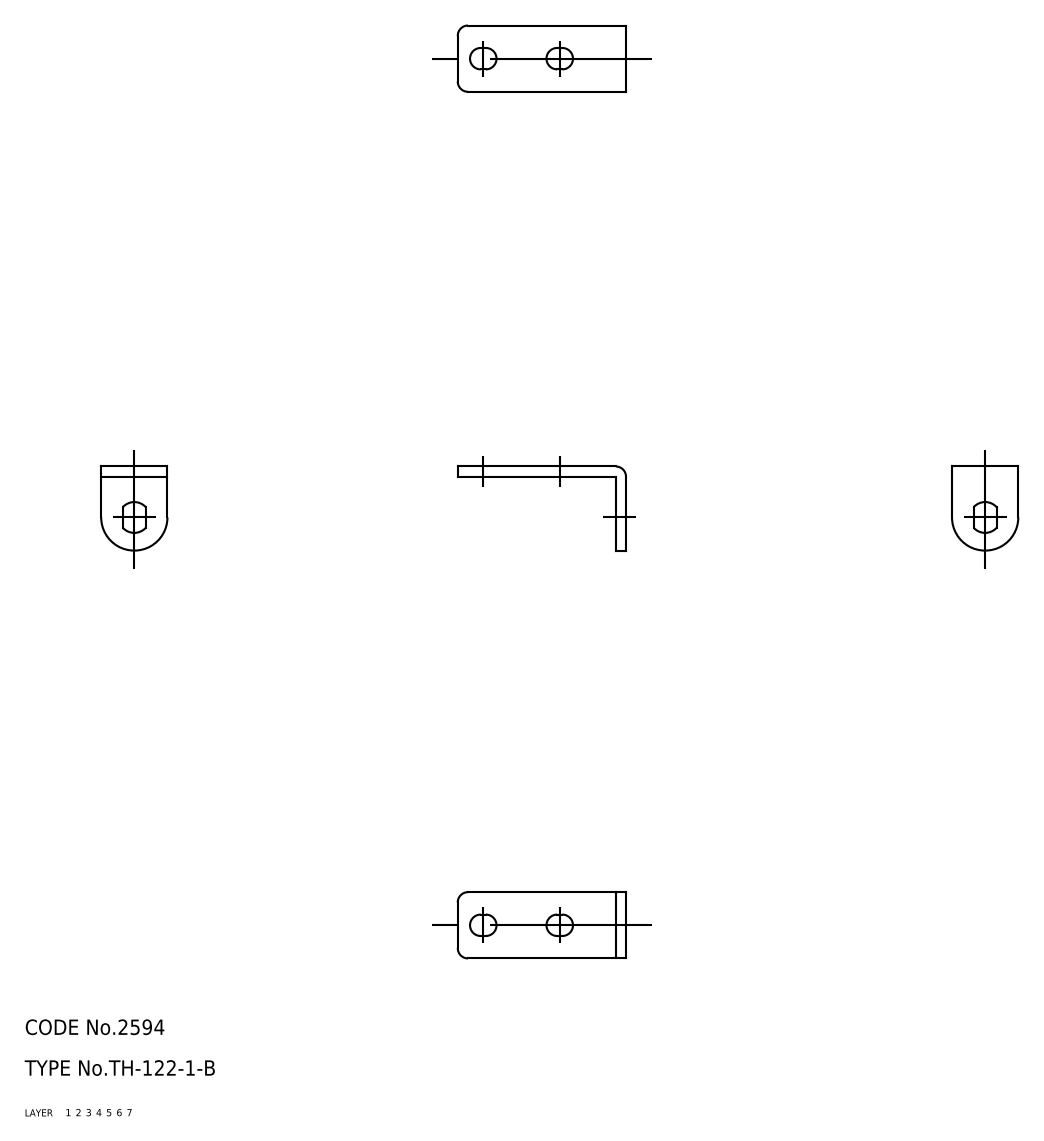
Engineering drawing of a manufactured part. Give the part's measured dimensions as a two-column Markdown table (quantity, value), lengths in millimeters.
| quantity | value |
| --- | --- |
| part name | 67109944 |
| STEP written by | CADfix (AUTOMOTIVE_DESIGN) |
| units | millimeters |
| bodies | 1 solid, 23 faces (0 planar, 0 cylindrical, 23 other) |
| overall size | 33 × 16.5 × 13 |
| volume | 1 063 mm³ |
| surface area | 1 386 mm² |
